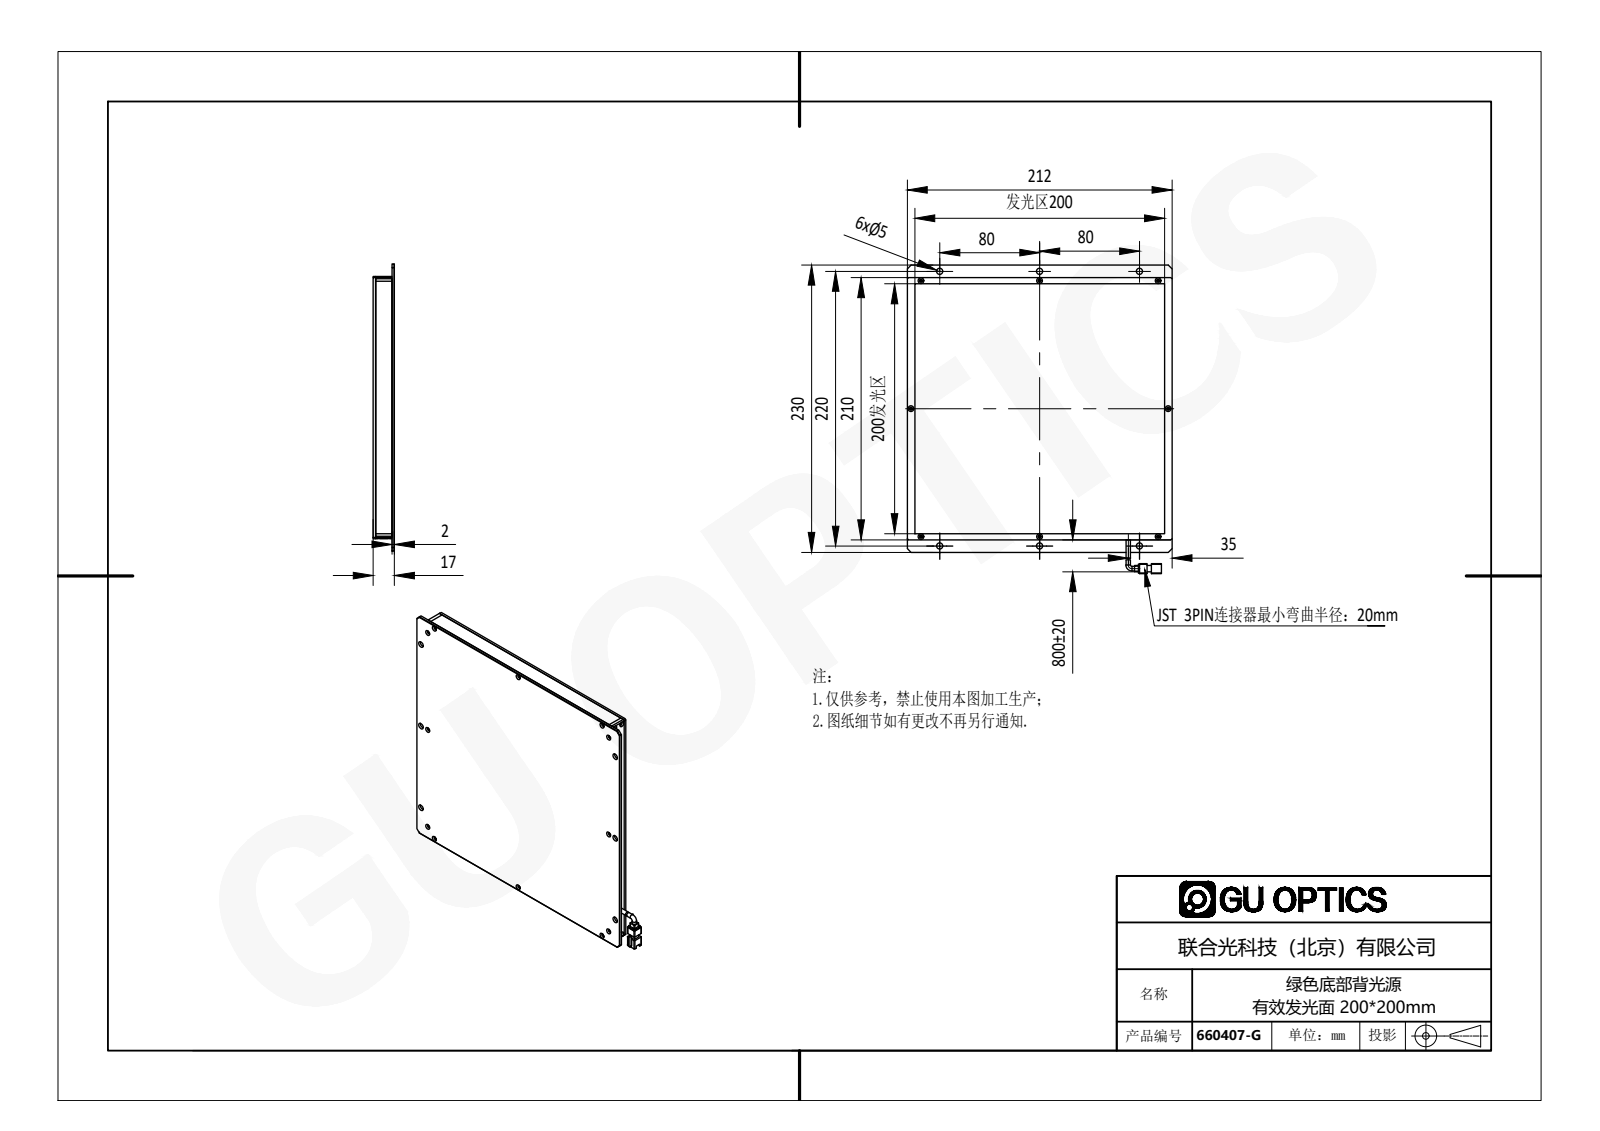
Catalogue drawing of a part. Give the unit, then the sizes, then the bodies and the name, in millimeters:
Units: millimetres
Overall size (bounding box): 247 × 212 × 20.3
Round holes (diameter × count): ⌀1.6 ×16, ⌀2.4 ×16, ⌀5 ×6
Round bosses / shafts (diameter × count): ⌀3.5 ×2
Partial cylindrical surfaces — rounded edges, fillets, slot ends (radius × count): R0.5 ×8, R1 ×4, R2 ×2, R1.6 ×1
Main face-to-face distances: 15, 2, 13, 3, 16, 18, 6, 206, 200, 5
Hole centre spacings: 95, 206, 10.97, 16.77, 27.46, 80, 80.35, 95.3
Volume: 283 962 mm³ · Surface area: 223 998 mm²
Bodies: 8 solids, 522 faces (199 planar, 149 cylindrical, 174 other)
Part name (STEP PRODUCT): 660407-G
STEP written by: SolidWorks 2016 (AUTOMOTIVE_DESIGN)
